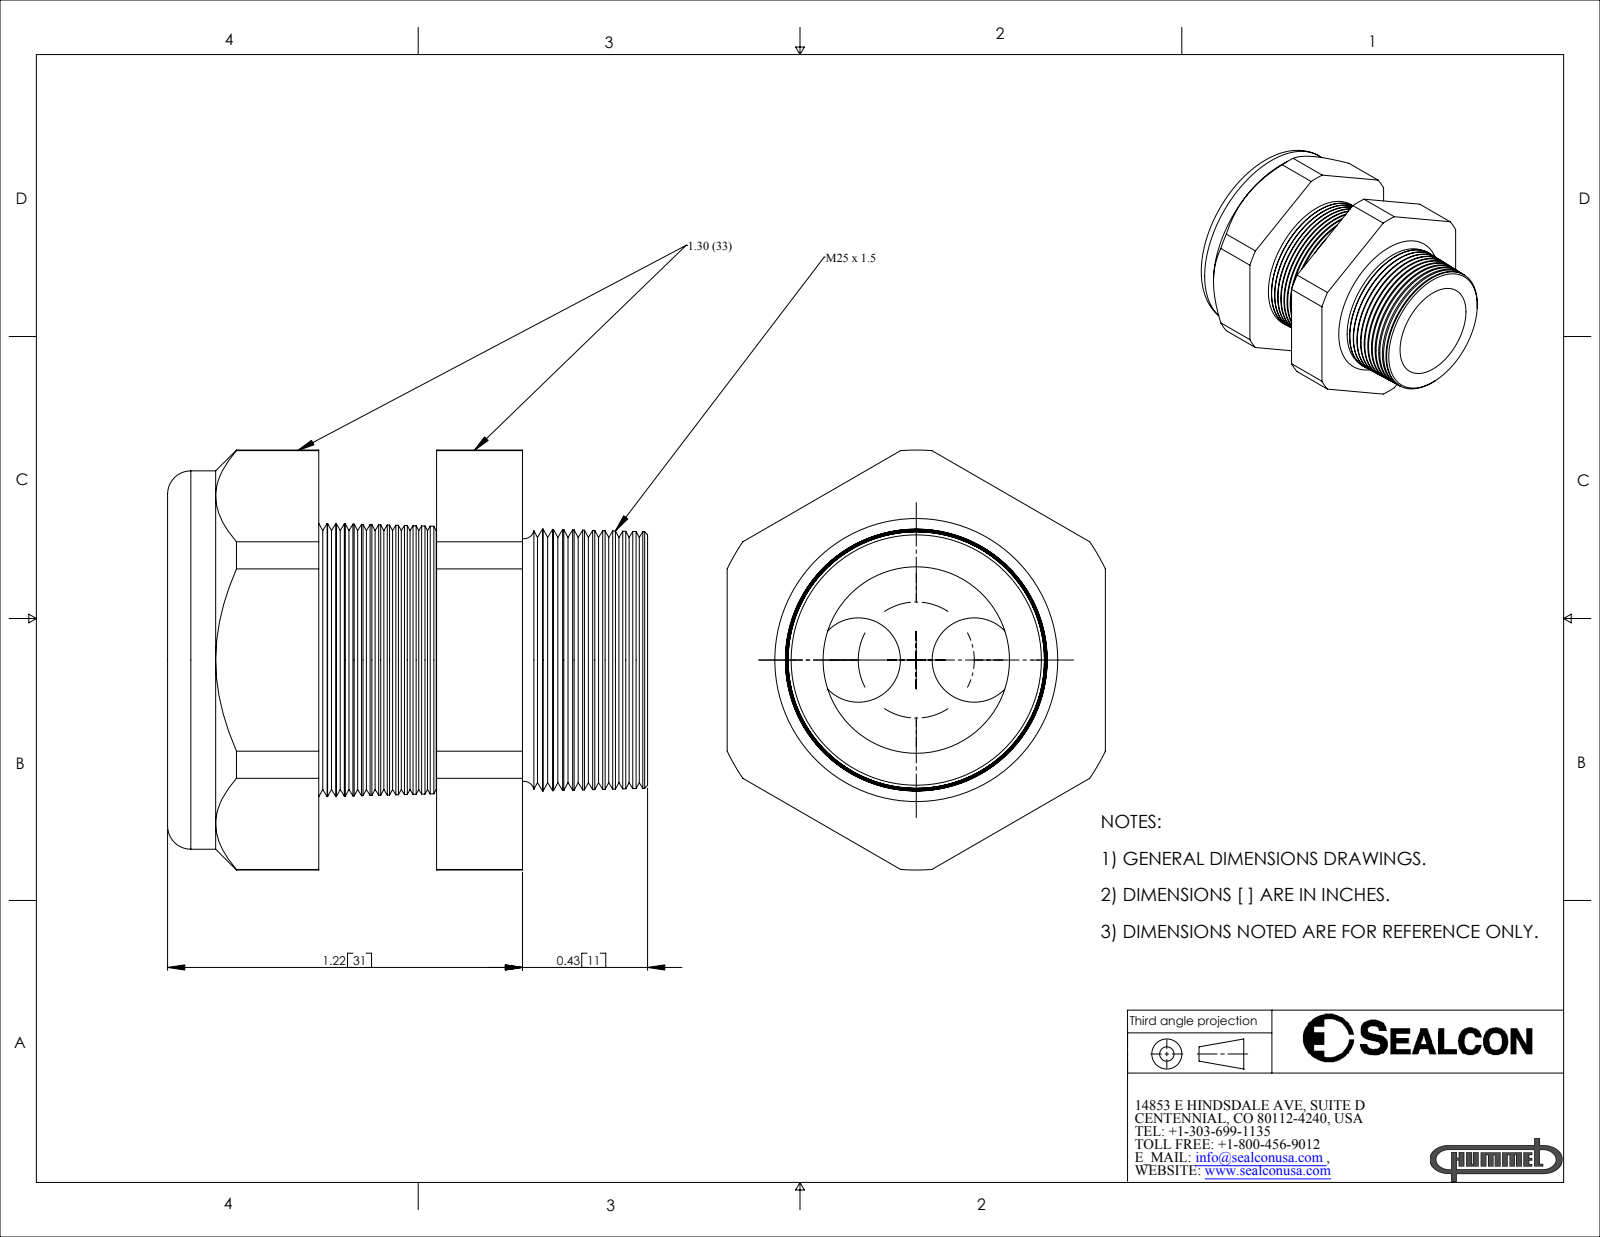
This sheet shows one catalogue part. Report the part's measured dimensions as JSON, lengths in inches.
{"part_name": "CD25M9-BK", "step_written_by": "SolidWorks 2007 (CONFIG_CONTROL_DESIGN)", "units": "inches", "bodies": {"solids": 2, "faces": 210, "planar": 20, "cylindrical": 24, "other": 166}, "overall_size": [1.65, 1.443, 1.3], "volume_in3": 1.147, "surface_area_in2": 16.89, "round_holes": [[0.29, 2], [0.69, 1], [0.71, 1]], "round_bosses_or_shafts": [[1.3, 1]], "partial_cylinders_radius": [[0.721, 1]], "face_to_face_distances": [1.3, 0.405, 0.7, 0.295, 0.52, 0.925, 1.22, 0.35, 0.17, 0.575], "hole_center_spacings": [0.2, 0.399]}
